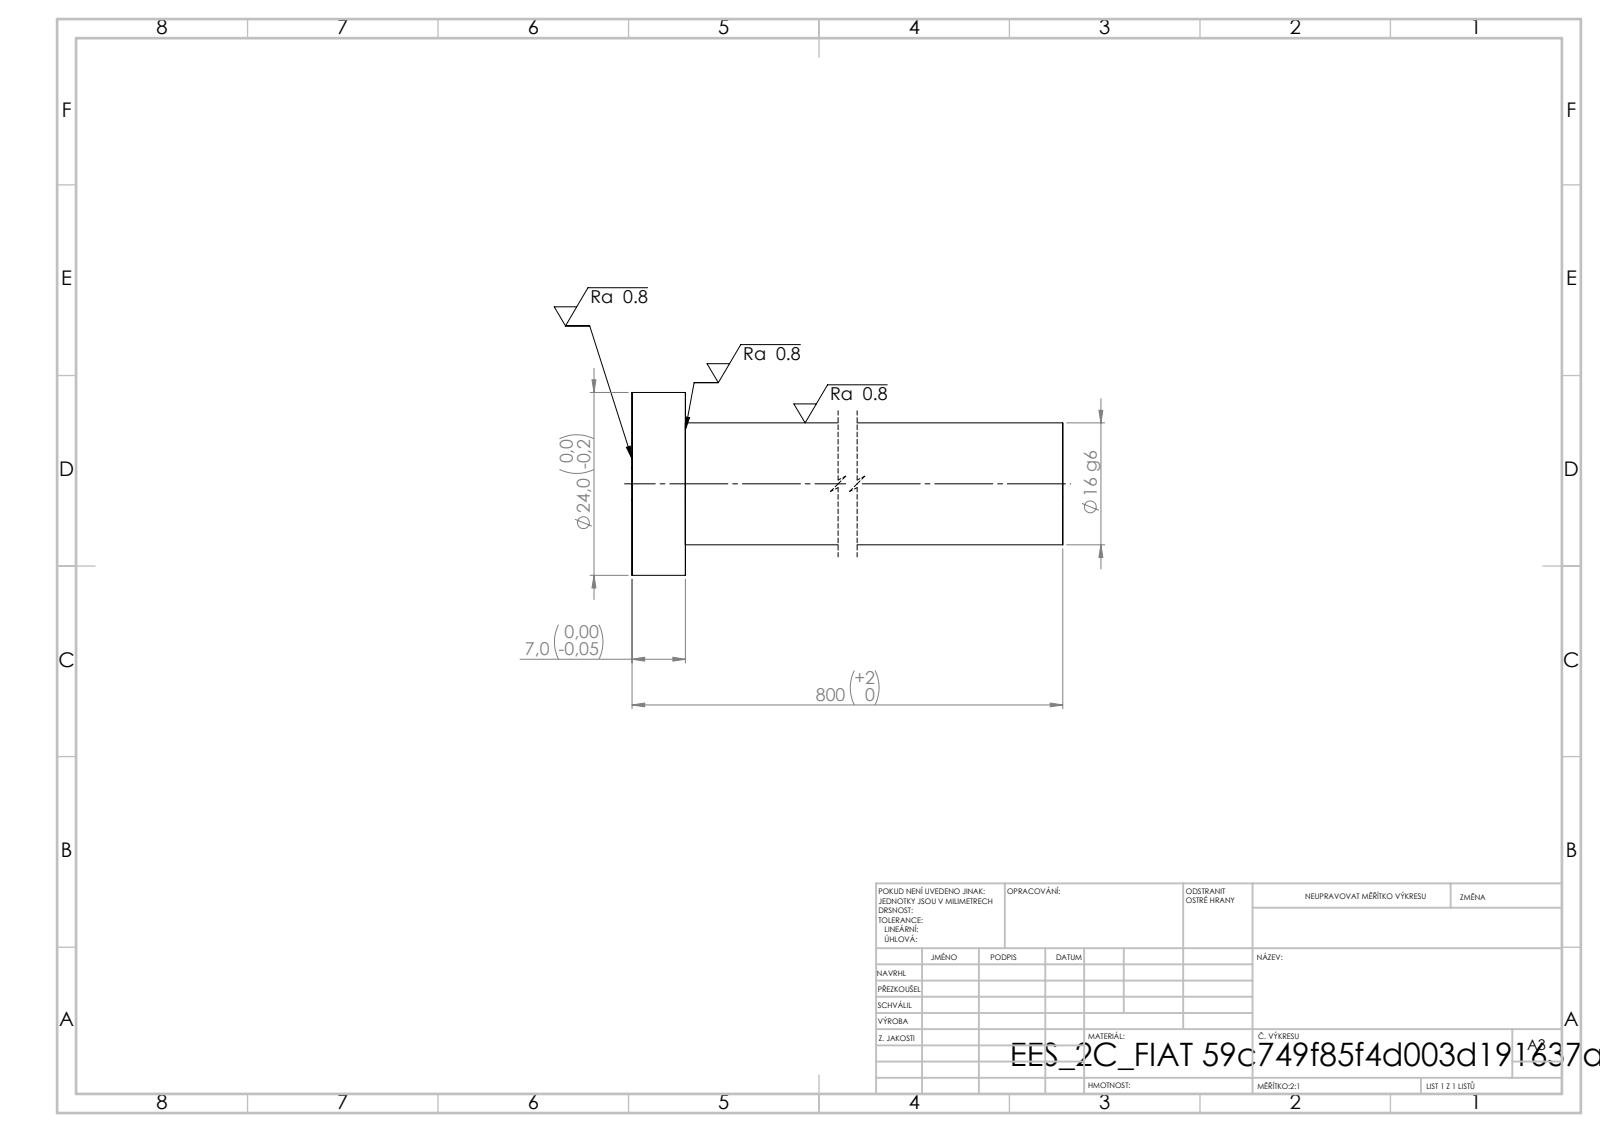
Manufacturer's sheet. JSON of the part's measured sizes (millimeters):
{"step_written_by": "SolidWorks 2019 (CONFIG_CONTROL_DESIGN)", "units": "millimeters", "bodies": {"solids": 1, "faces": 7, "planar": 3, "cylindrical": 4, "other": 0}, "overall_size": [800, 24, 24], "volume_mm3": 162609, "surface_area_mm2": 41293, "round_bosses_or_shafts": [[24, 1], [16, 1]], "face_to_face_distances": [7, 800, 793]}
